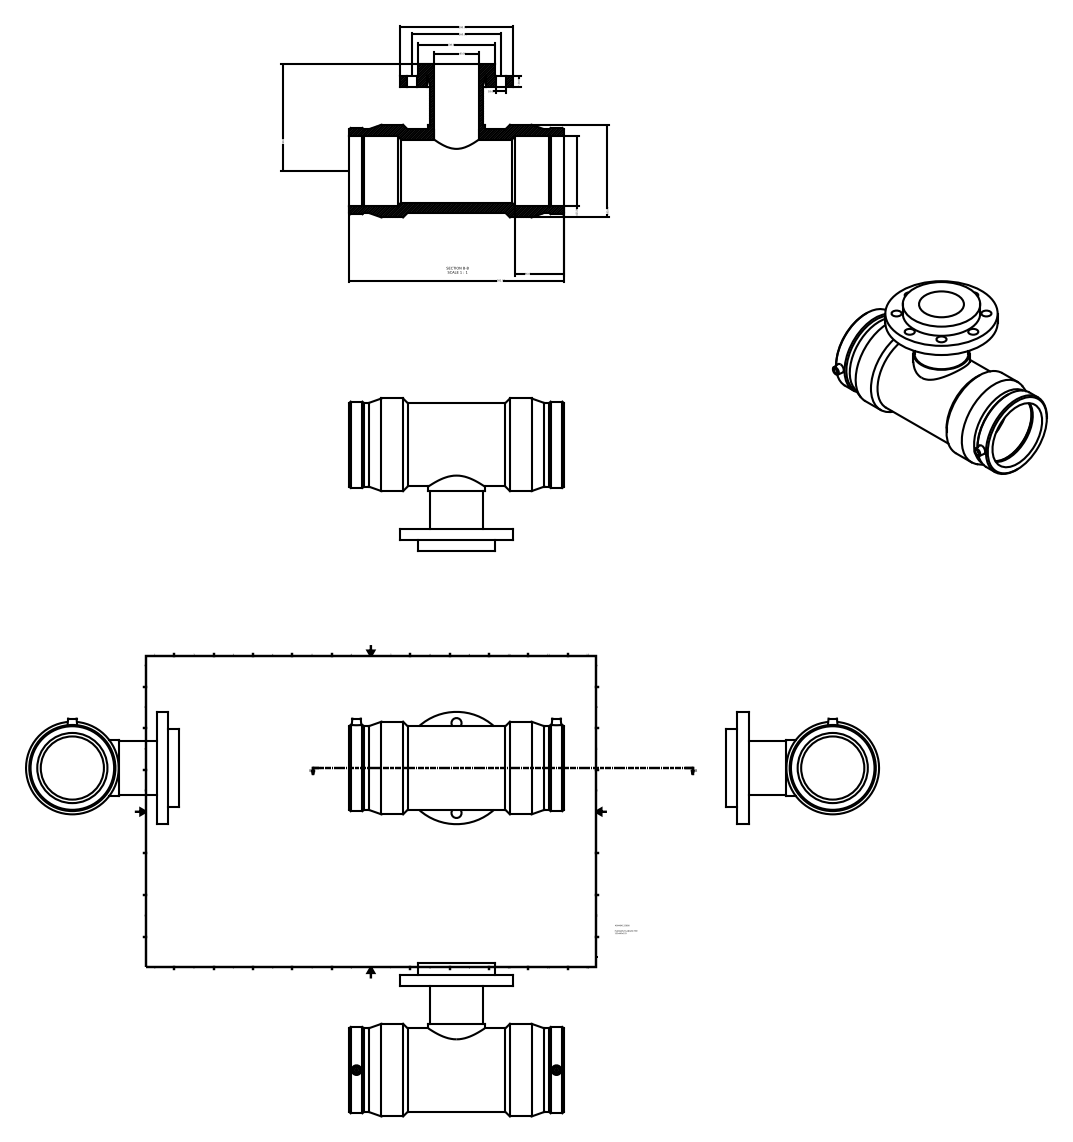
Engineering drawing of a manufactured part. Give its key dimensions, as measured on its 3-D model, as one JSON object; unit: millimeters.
{"part_name": "499404125080", "step_written_by": "Autodesk Inventor 2015 (AUTOMOTIVE_DESIGN)", "units": "millimeters", "bodies": {"solids": 1, "faces": 60, "planar": 14, "cylindrical": 30, "other": 16}, "overall_size": [382, 272.5, 200], "volume_mm3": 3670000, "surface_area_mm2": 484961, "round_holes": [[18, 8], [10, 2], [80, 1], [104, 1], [112.5, 1], [125, 1]], "round_bosses_or_shafts": [[4, 2], [200, 1], [165, 1], [153.45, 1], [148.85, 1], [148.5, 1], [138, 1], [100, 1]], "face_to_face_distances": [20, 40, 382, 107.5, 87.5, 67.5, 27.02, 354.98, 327.96, 14], "hole_center_spacings": [61.23, 80, 113.14, 147.82, 160, 356.2]}
